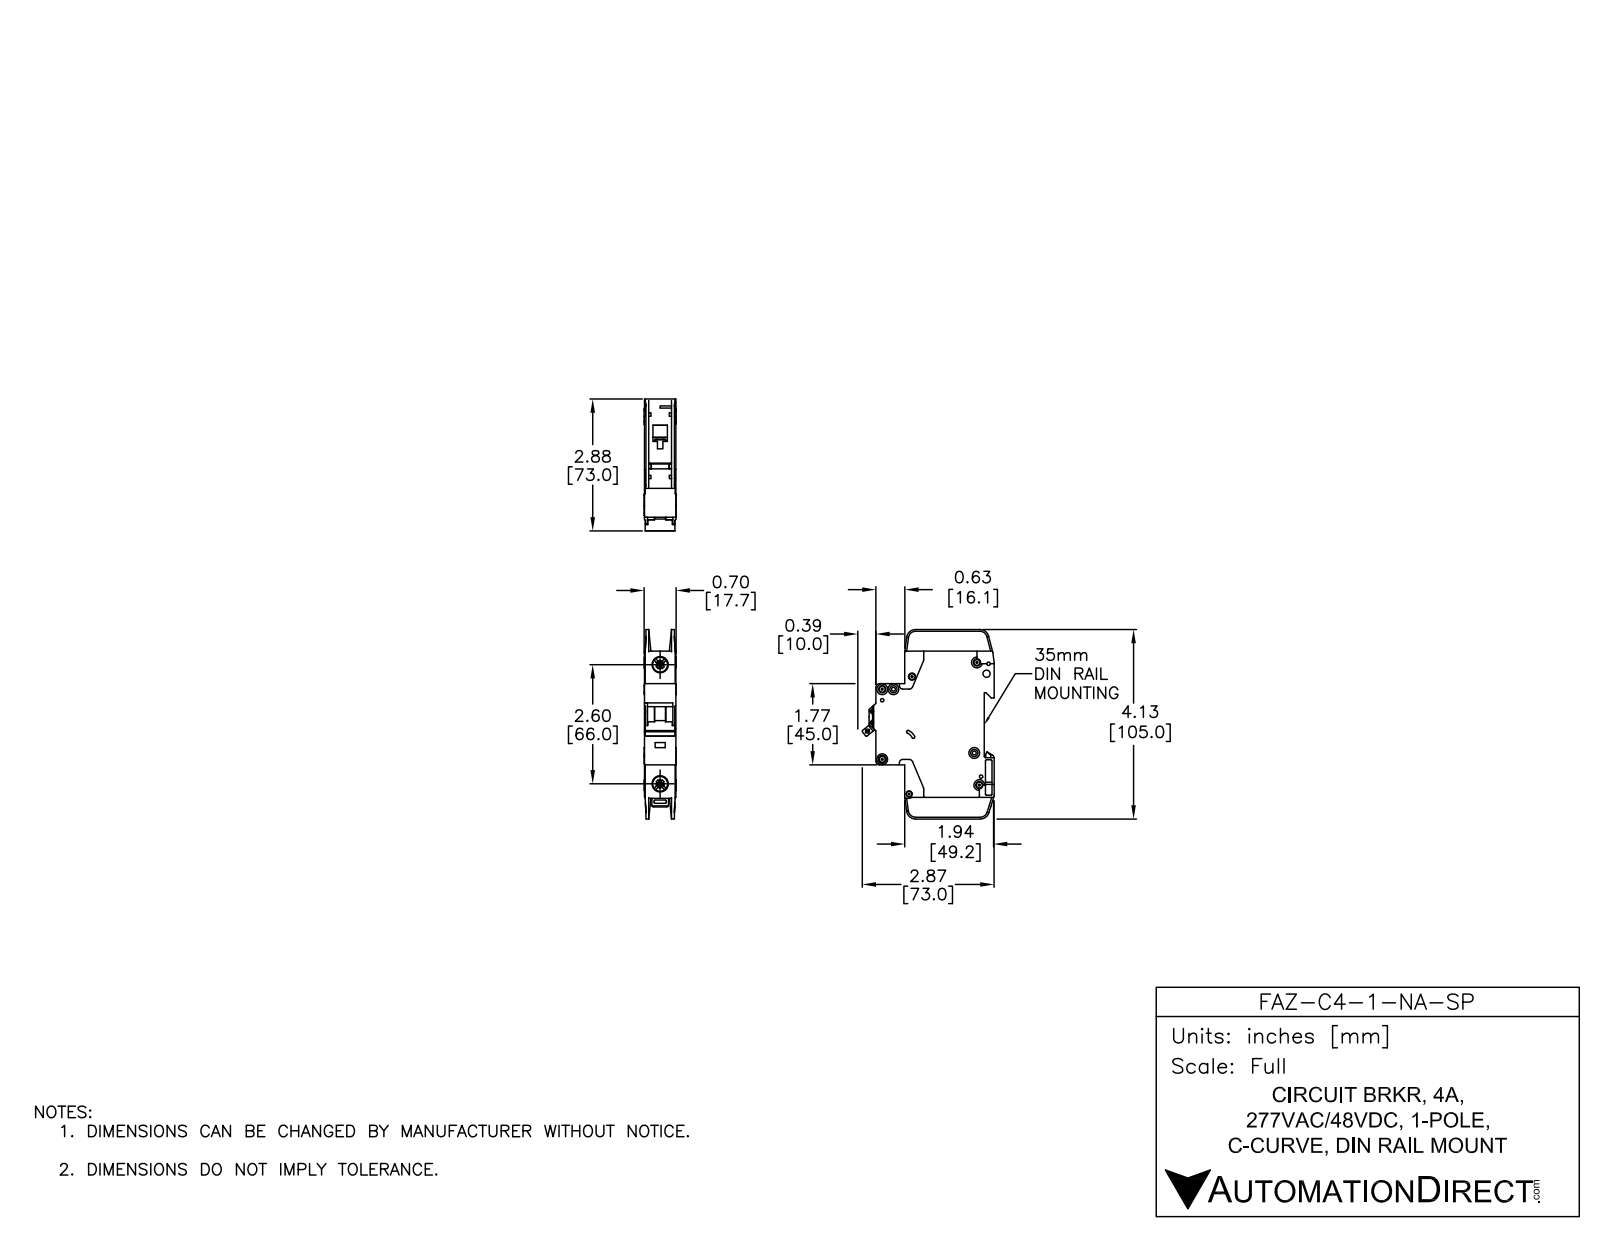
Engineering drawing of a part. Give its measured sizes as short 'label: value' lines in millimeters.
name: FAZ-C4-1-NA-SP
written by: SolidWorks 2014 (AUTOMOTIVE_DESIGN)
unit: mm
bodies: 3 solids, 784 faces (409 planar, 263 cylindrical, 112 other)
size: 105 × 73.04 × 17.7
volume: 77 695 mm³; area: 24 740 mm²
holes: 7× ⌀3.6, 2× ⌀1.09, 2× ⌀1.5, 2× ⌀4, 2× ⌀7.15, 2× ⌀8.2, 1× ⌀1.9, 1× ⌀2.15, 1× ⌀2.2, 1× ⌀2.55, 1× ⌀3.3, 1× ⌀3.4
bosses: 7× ⌀6, 1× ⌀2.5
rounds: 29× R0.25, 18× R0.5, 10× R1, 10× R2, 5× R5, 4× R4, 3× R1.8, 2× R0.2
face distances: 17.5, 15.05, 0.7, 2.45, 1.75, 15.75, 13.3, 14, 12.6, 2
hole spacings: 6.2, 5.19, 6.1, 8.19, 8.56, 8.7, 11.11, 12.45
